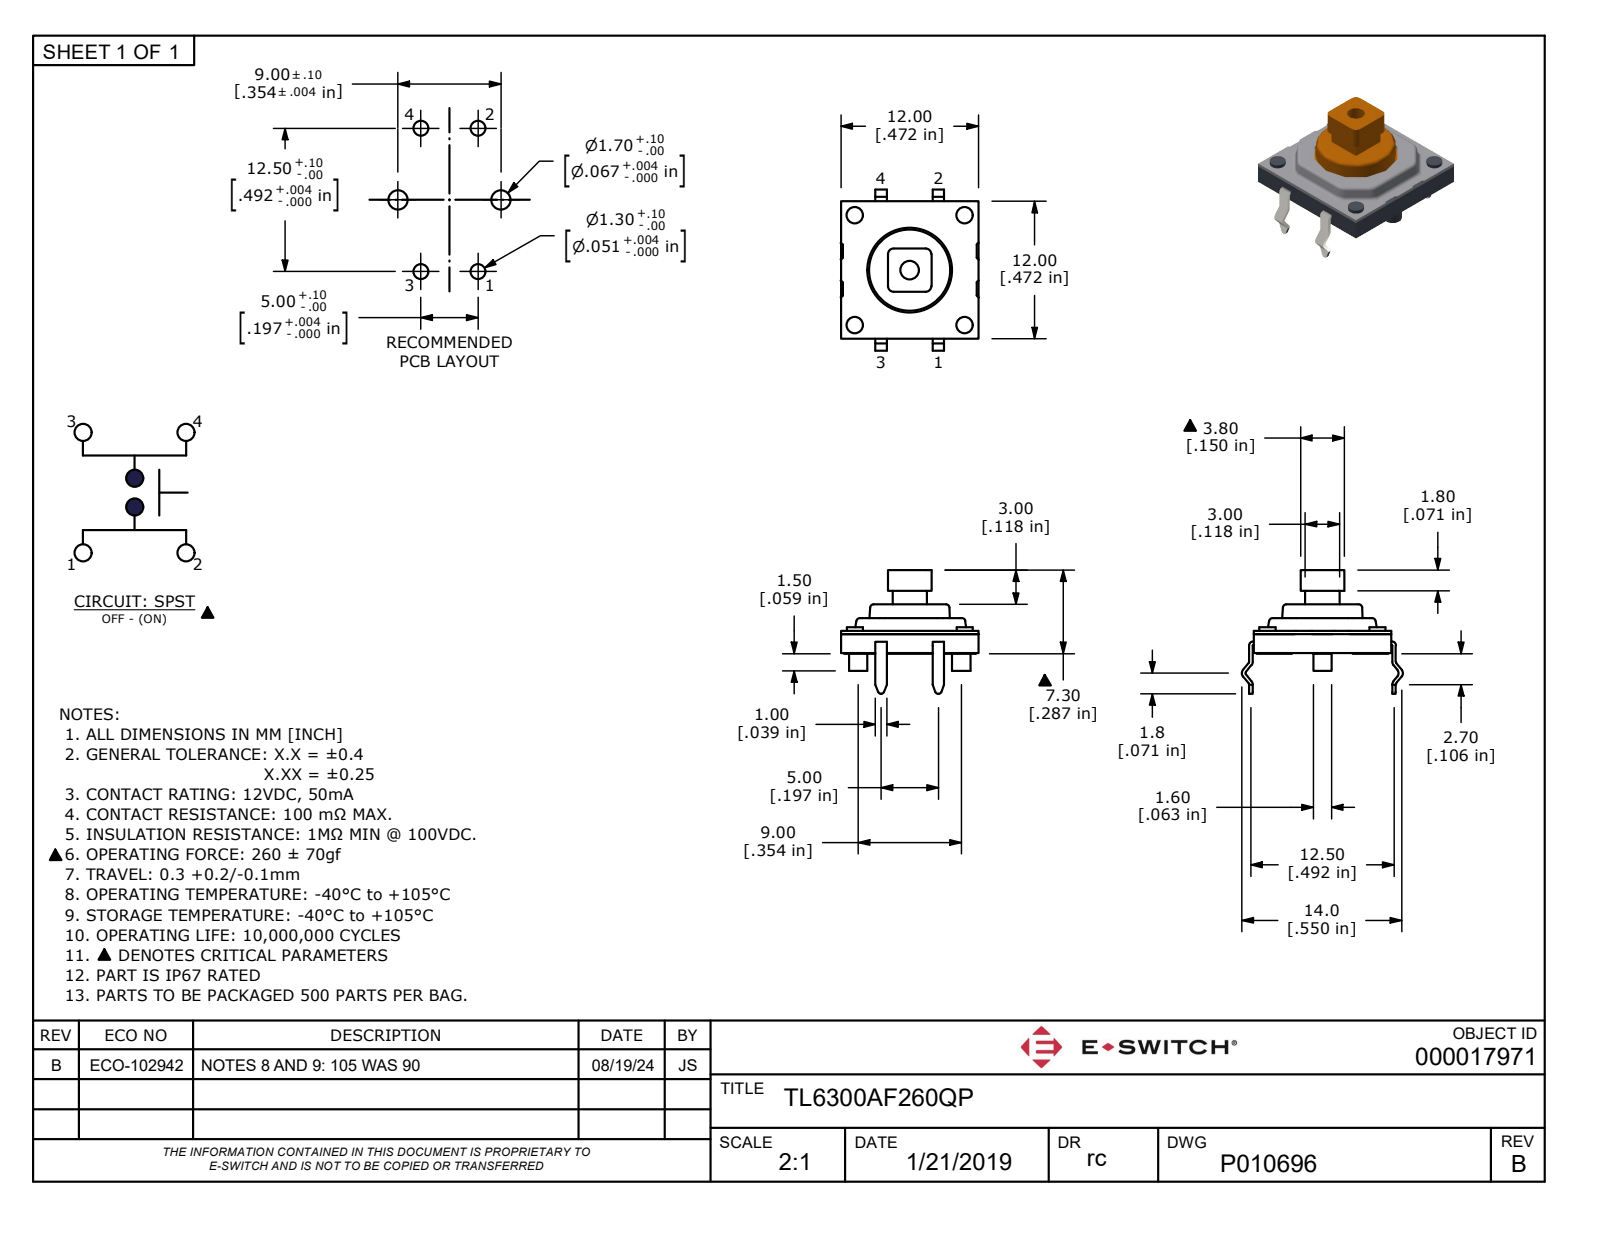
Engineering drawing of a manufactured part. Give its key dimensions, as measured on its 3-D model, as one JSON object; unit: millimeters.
{"part_name": "P010696_Shrinkwrap_1", "step_written_by": "Autodesk Inventor 2020 (AUTOMOTIVE_DESIGN)", "units": "millimeters", "bodies": {"solids": 3, "faces": 404, "planar": 165, "cylindrical": 148, "other": 91}, "overall_size": [14.1, 12, 10.8], "volume_mm3": 410, "surface_area_mm2": 1011, "round_holes": [[1.2, 4], [1.6, 1], [7.4, 1]], "round_bosses_or_shafts": [[1.4, 4], [1.6, 2]], "partial_cylinders_radius": [[0.2, 21], [0.3, 20], [0.1, 16], [0.5, 12], [0.3, 9], [0.7, 8], [1, 8], [0.5, 7]], "face_to_face_distances": [1.7, 1.1, 0.6, 0.5, 1.5, 2.2, 2.7, 0.8, 1.7, 2], "hole_center_spacings": [6.8, 9.6, 13.6]}
